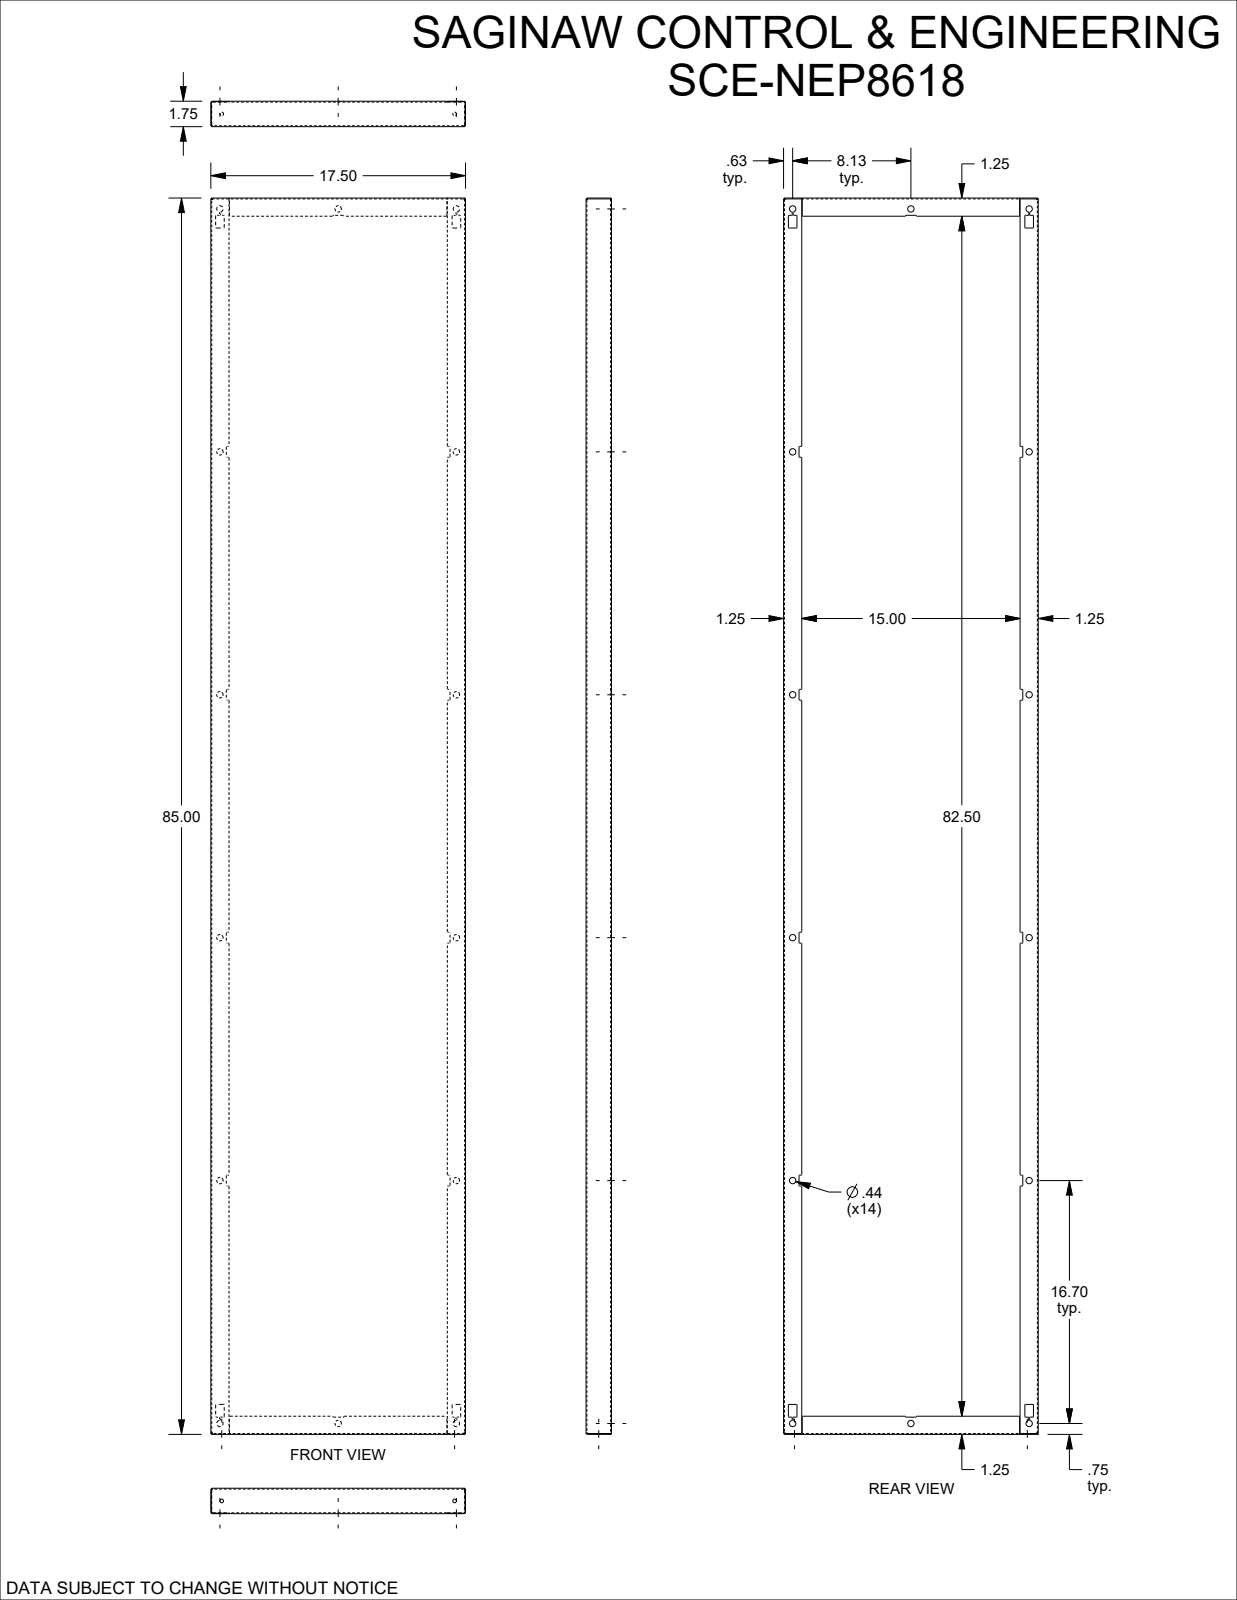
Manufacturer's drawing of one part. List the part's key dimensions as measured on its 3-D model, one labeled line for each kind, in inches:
Part name (STEP PRODUCT): SCE-NEP8618
STEP written by: SolidWorks 2023 (AUTOMOTIVE_DESIGN)
Units: inches
Bodies: 1 solid, 170 faces (84 planar, 86 cylindrical, 0 other)
Overall size (bounding box): 85 × 17.5 × 1.75
Volume: 123.6 in³ · Surface area: 4 146 in²
Round holes (diameter × count): ⌀0.437 ×14
Partial cylindrical surfaces — rounded edges, fillets, slot ends (radius × count): R0.03 ×72
Main face-to-face distances: 0.06, 1.69, 17.44, 1.75, 1.63, 17.5, 17.38, 84.94, 85, 84.88
Hole centre spacings: 16.7, 23.301, 33.4, 37.143, 16.25, 50.1, 52.669, 18.572
